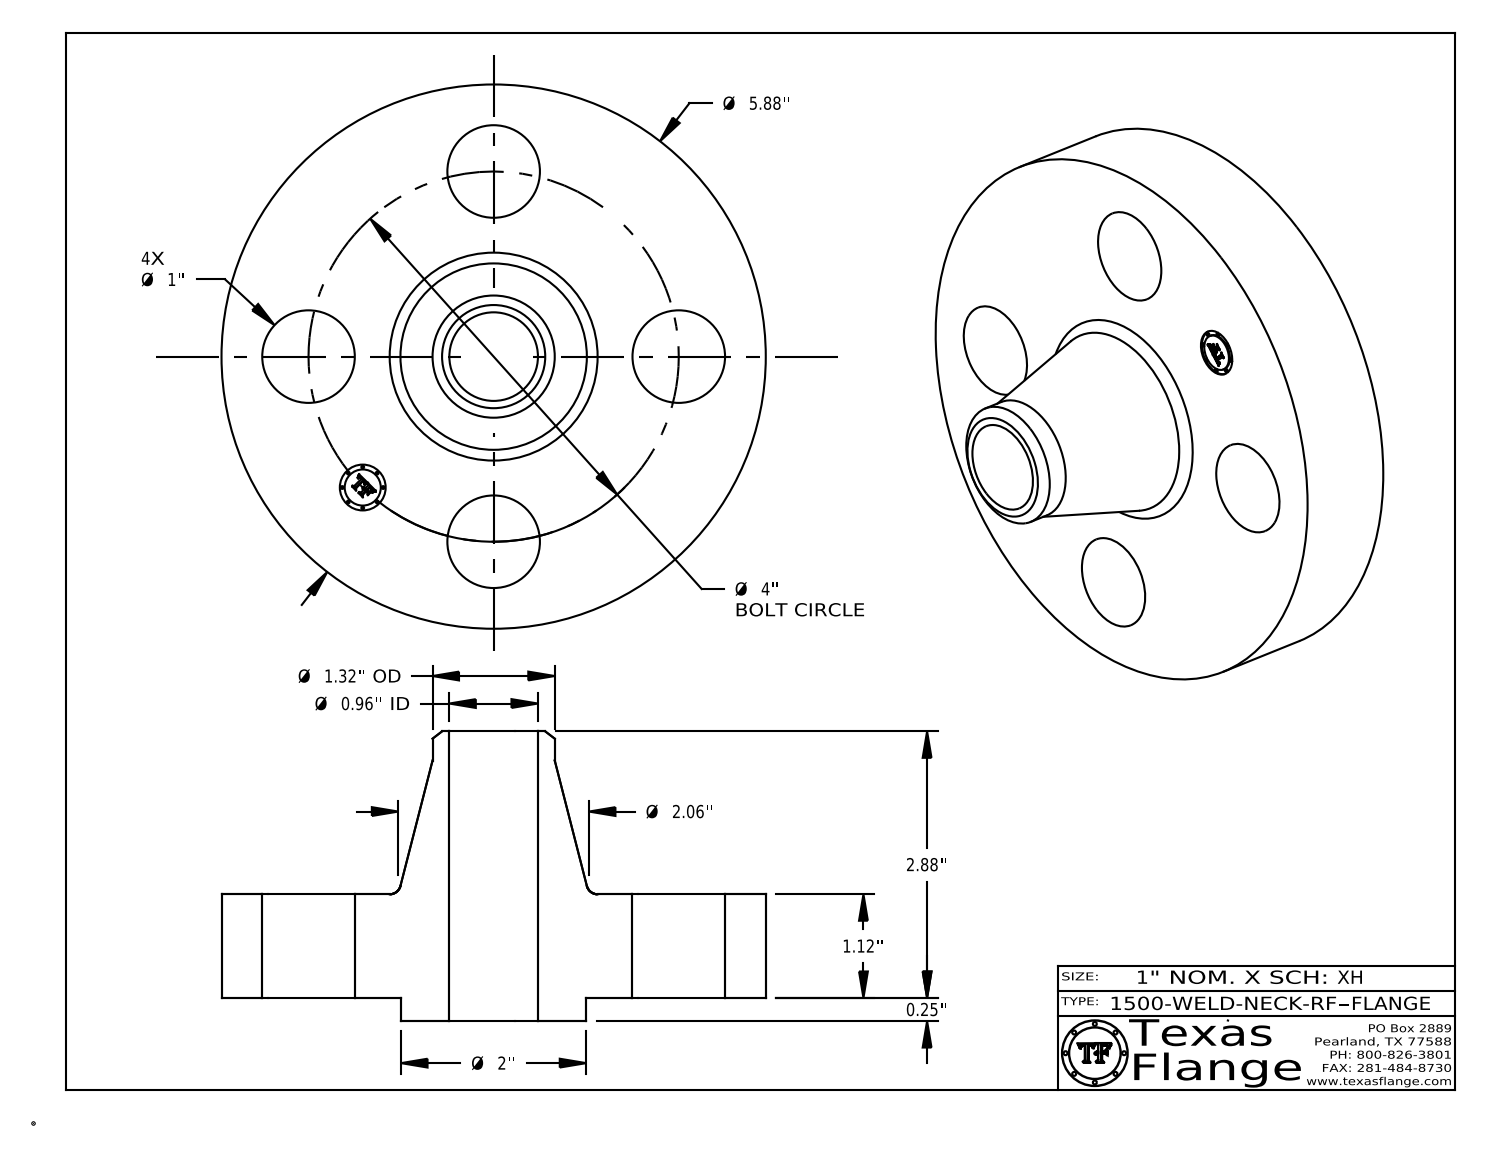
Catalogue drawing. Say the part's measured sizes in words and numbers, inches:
The part is named "1500-WELD-NECK-RF". Its 3-D file was written by "CATIA V5 STEP AP214 (AUTOMOTIVE_DESIGN)". It is 1 solid with 411 faces: 369 planar, 36 cylindrical and 6 other. Overall it measures 5.88 by 5.88 by 3.13 inches. Its volume is 29.15 cubic inches and its surface area 99.29 square inches. Round holes: 4 of diameter 1, 1 of diameter 0.495, 1 of diameter 0.957. Round bosses or shafts: 8 of diameter 0.03, 1 of diameter 5.88, 1 of diameter 2, 1 of diameter 1.32, 1 of diameter 0.39. The main face-to-face distances are 1.12, 0.25, 1.37, 3.13, 2.88, 1.76, 0.015, 1.355, 1.105, 1.775. The hole center spacings are 2, 2.828, 1.531, 3.695, 4.
